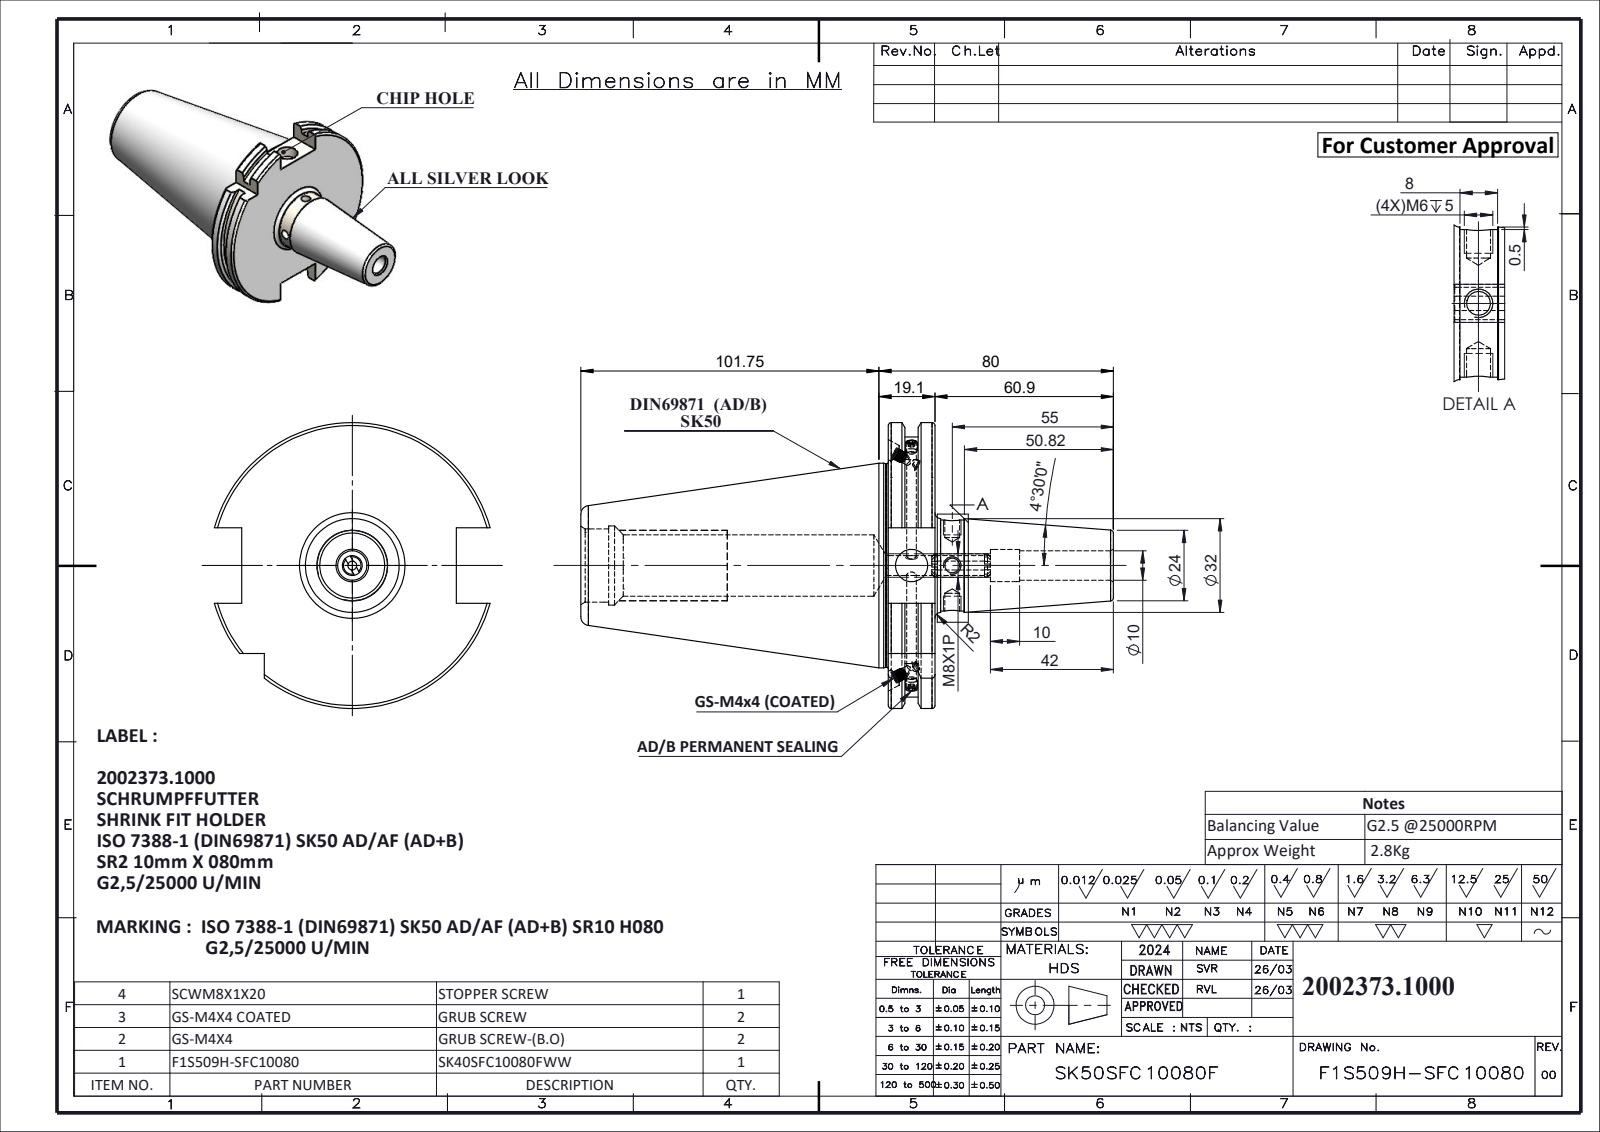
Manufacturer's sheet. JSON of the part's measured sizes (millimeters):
{"part_name": "F1S509H-SFC10080; SCWM8X1; SK50SFC10080FWW; GS-M4X4_DIN 913 - M4 x 4-N (+1 more)", "step_written_by": "SolidWorks 2024 (AUTOMOTIVE_DESIGN)", "units": "millimeters", "bodies": {"solids": 6, "faces": 296, "planar": 81, "cylindrical": 91, "other": 124}, "overall_size": [181.75, 97.5, 94.05], "volume_mm3": 359310, "surface_area_mm2": 52959, "round_holes": [[3.2, 2], [5, 2], [6, 2], [11, 2], [3, 1], [3.3, 1], [6.8, 1], [10, 1], [21, 1], [25, 1], [27, 1], [32, 1]], "round_bosses_or_shafts": [[4, 4], [2.9, 2], [69.85, 1], [69.45, 1], [31, 1], [8, 1]], "partial_cylinders_radius": [[44.9, 1], [48.75, 1]], "face_to_face_distances": [15.9, 5.65, 10.25, 10.14, 4.49, 5.76, 104.95, 110.6, 115.09, 120.85], "hole_center_spacings": [13.9]}
